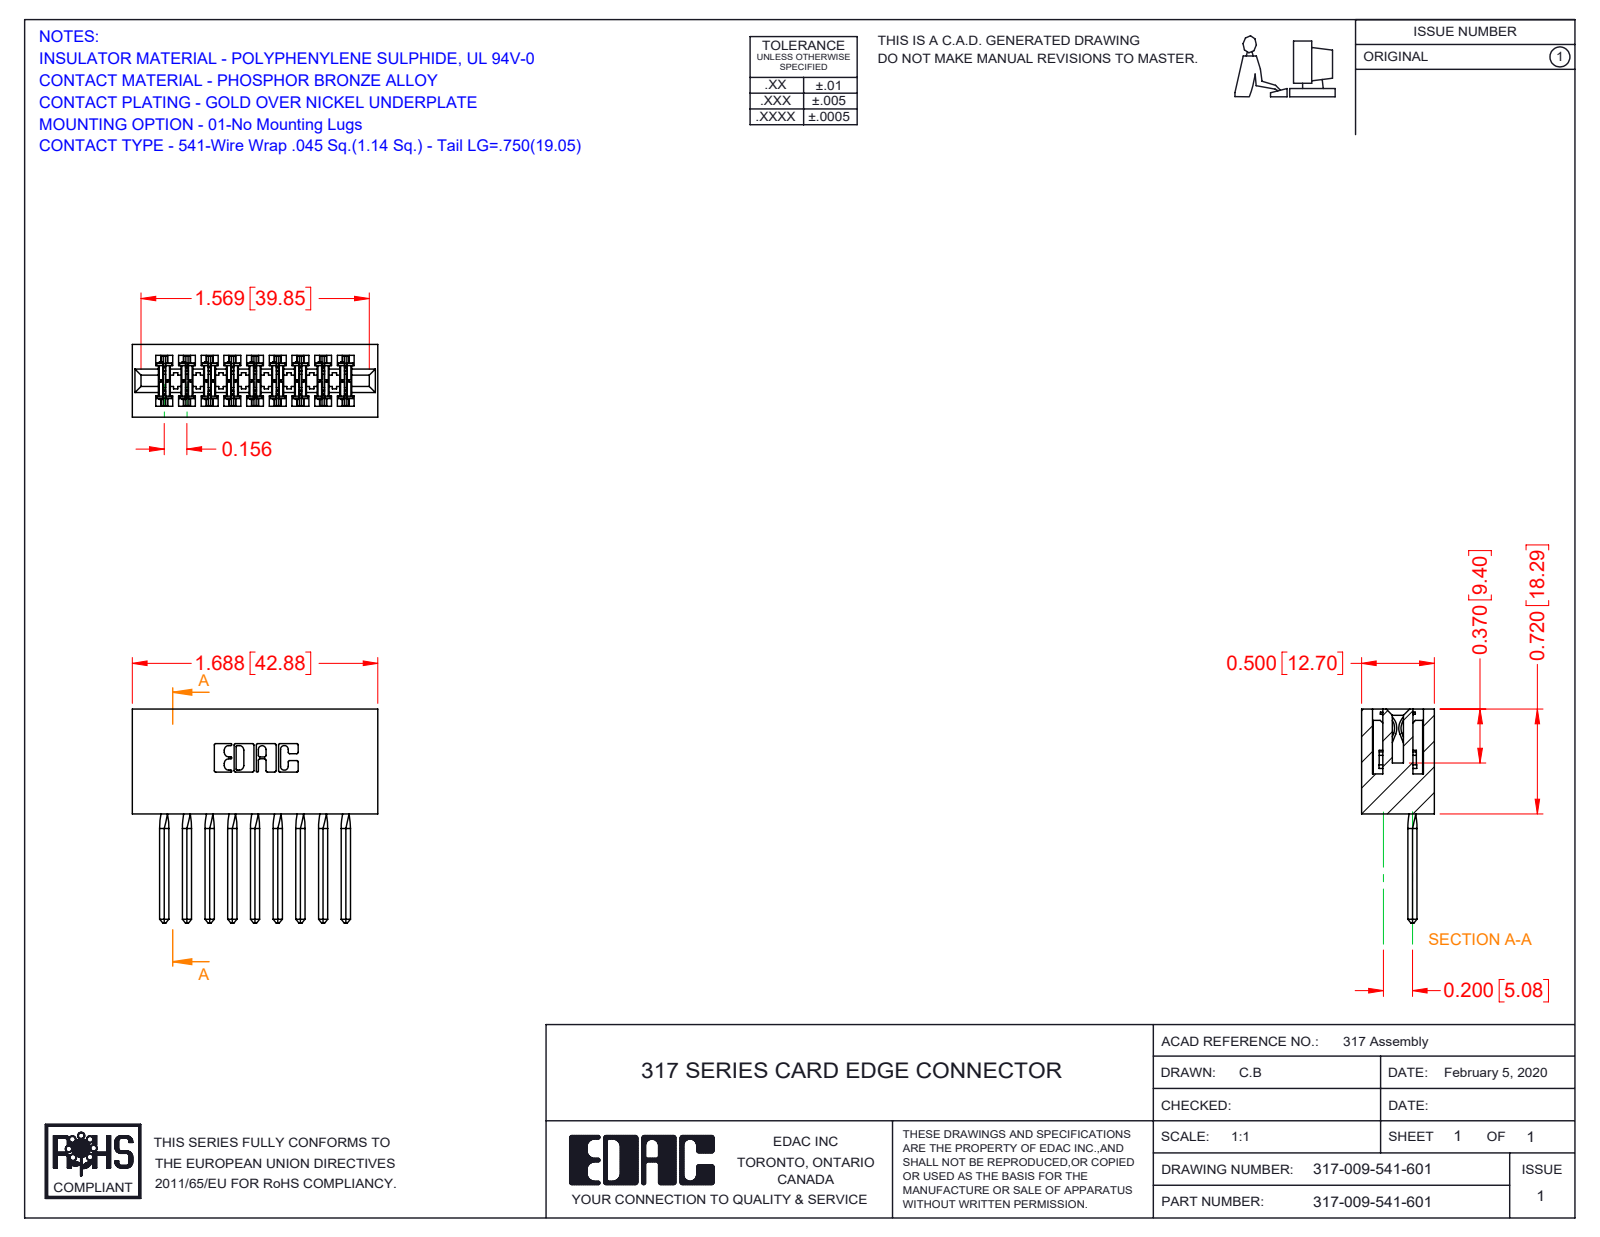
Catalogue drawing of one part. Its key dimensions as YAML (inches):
part_name: "317-290-002_541; 317-009-541-601; 317 Part_Lugless"
step_written_by: "SolidWorks 2016 (CONFIG_CONTROL_DESIGN)"
units: inches
bodies: {solids: 10, faces: 1458, planar: 1166, cylindrical: 256, other: 36}
overall_size: [1.688, 1.47, 0.5]
volume: 0.466
surface_area: 15.34
partial_cylinders:
  - {radius: 0.01, count: 22}
  - {radius: 0.015, count: 18}
  - {radius: 0.007, count: 6}
  - {radius: 0.031, count: 6}
  - {radius: 0.026, count: 3}
  - {radius: 0.095, count: 2}
  - {radius: 0.1, count: 2}
  - {radius: 0.11, count: 2}
face_to_face_distances: [0.5, 0.075, 0.425, 0.11, 0.156, 0.065, 0.22, 0.624, 0.312, 0.331]
